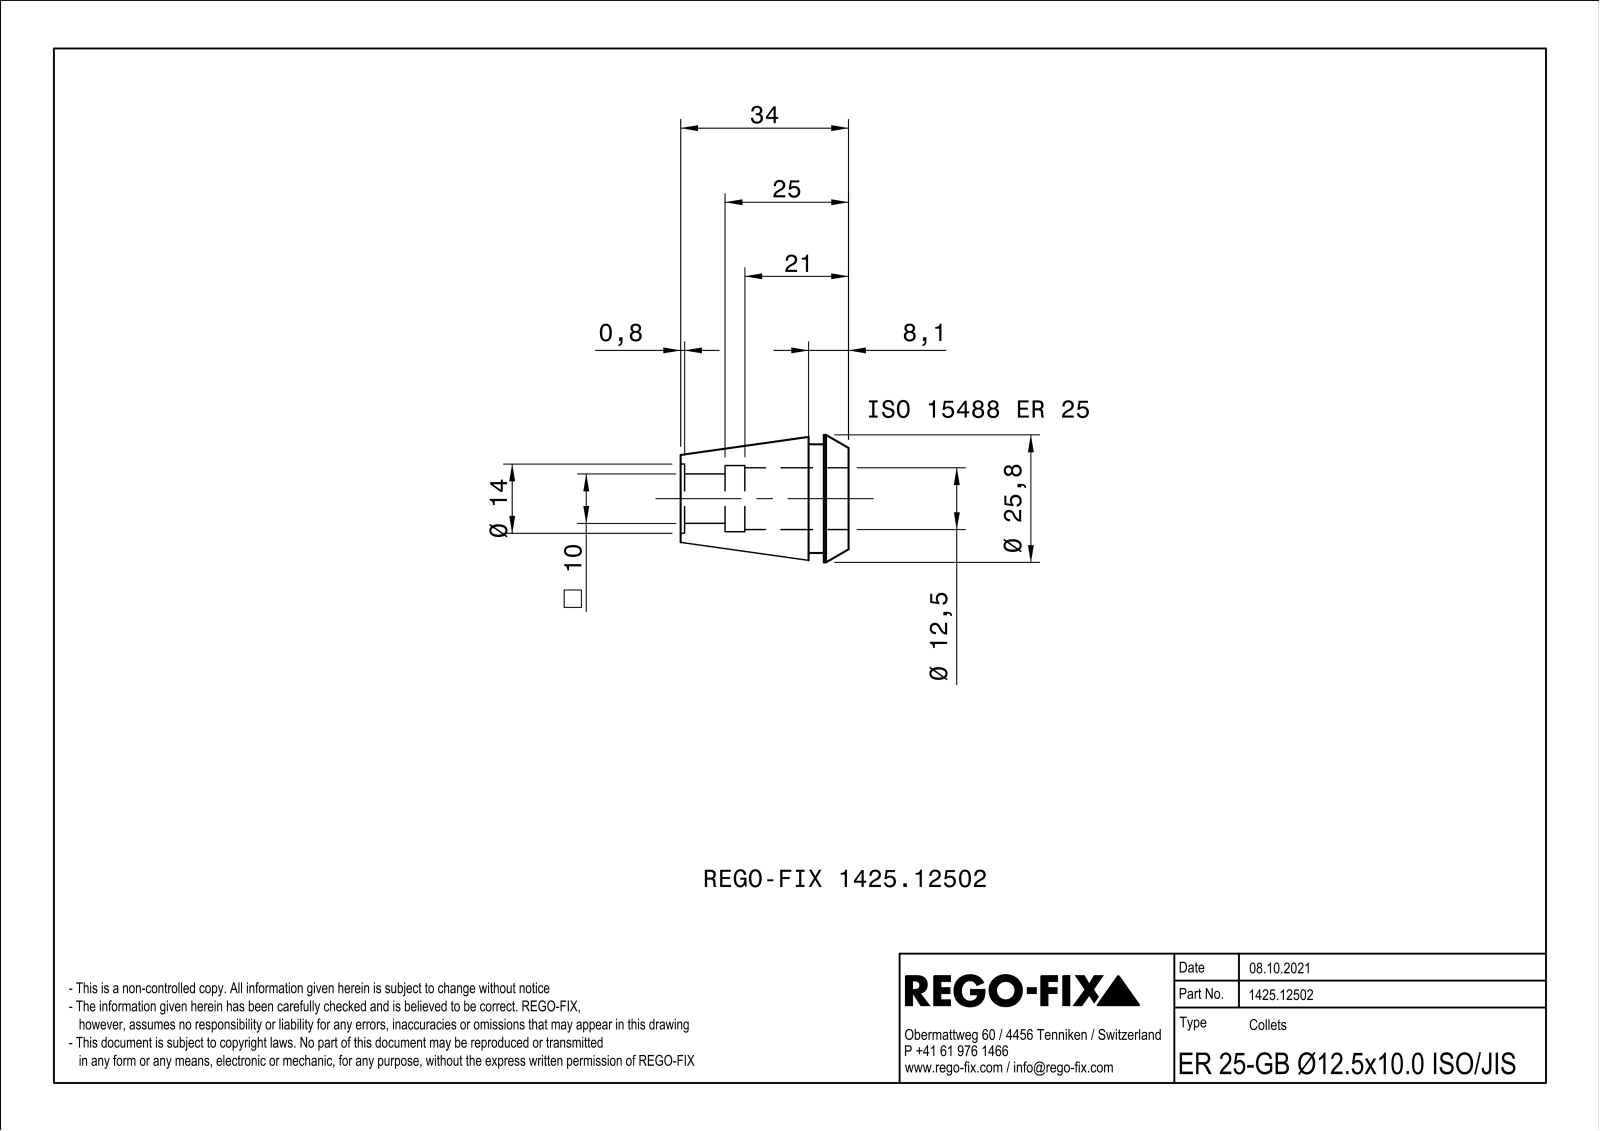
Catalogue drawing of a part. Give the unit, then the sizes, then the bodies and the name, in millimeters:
Units: millimetres
Overall size (bounding box): 34 × 25.79 × 25.79
Round holes (diameter × count): ⌀12.5 ×1, ⌀13.4 ×1
Round bosses / shafts (diameter × count): ⌀25.8 ×1, ⌀22 ×1
Partial cylindrical surfaces — rounded edges, fillets, slot ends (radius × count): R5.65 ×1, R6.5 ×1
Main face-to-face distances: 0.8, 5, 4.85, 5.65, 34, 29, 8.1, 3.1, 25.9, 10.5
Volume: 7 680 mm³ · Surface area: 6 138 mm²
Bodies: 1 solid, 132 faces (60 planar, 32 cylindrical, 40 other)
Part name (STEP PRODUCT): NOCUT
STEP written by: SIEMENS PLM Software Solid Edge ST10 (AUTOMOTIVE_DESIGN)
